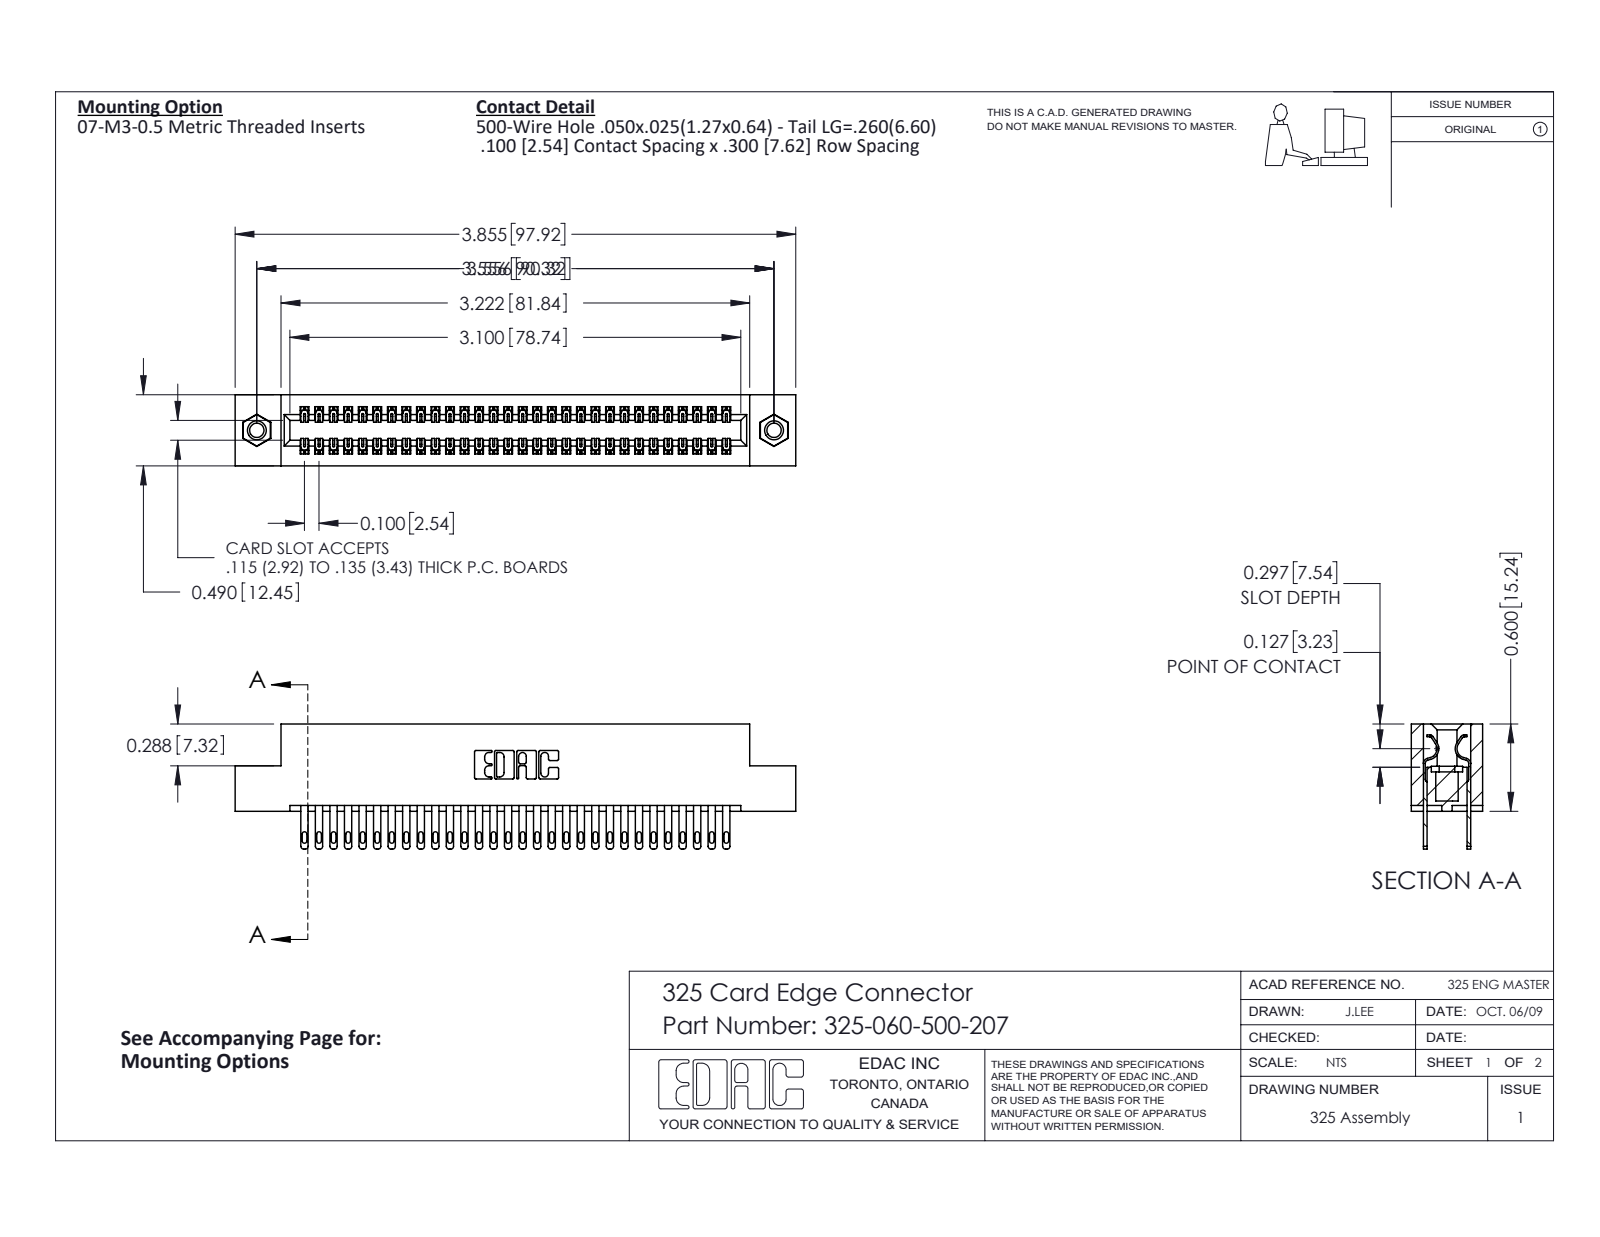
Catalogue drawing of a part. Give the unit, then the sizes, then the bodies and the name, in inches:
Units: inches
Overall size (bounding box): 3.855 × 0.86 × 0.49
Round holes (diameter × count): ⌀0.098 ×2, ⌀0.125 ×2, ⌀0.16 ×2
Round bosses / shafts (diameter × count): ⌀0.155 ×2
Partial cylindrical surfaces — rounded edges, fillets, slot ends (radius × count): R0.006 ×90, R0.016 ×60, R0.02 ×60, R0.01 ×22, R0.007 ×6, R0.031 ×6, R0.026 ×3, R0.014 ×2
Main face-to-face distances: 0.083, 0.407, 0.3, 0.107, 0.383, 0.025, 0.49, 0.325, 0.275, 0.04
Hole centre spacings: 3.556
Volume: 0.775 in³ · Surface area: 24.4 in²
Bodies: 63 solids, 3054 faces (1902 planar, 1136 cylindrical, 16 other)
Part name (STEP PRODUCT): 345-250-001_345-250-005-103; 325 Part_TI; 325-060-500-207; 325-292-001_325-293-100
STEP written by: SolidWorks 2016 (CONFIG_CONTROL_DESIGN)
